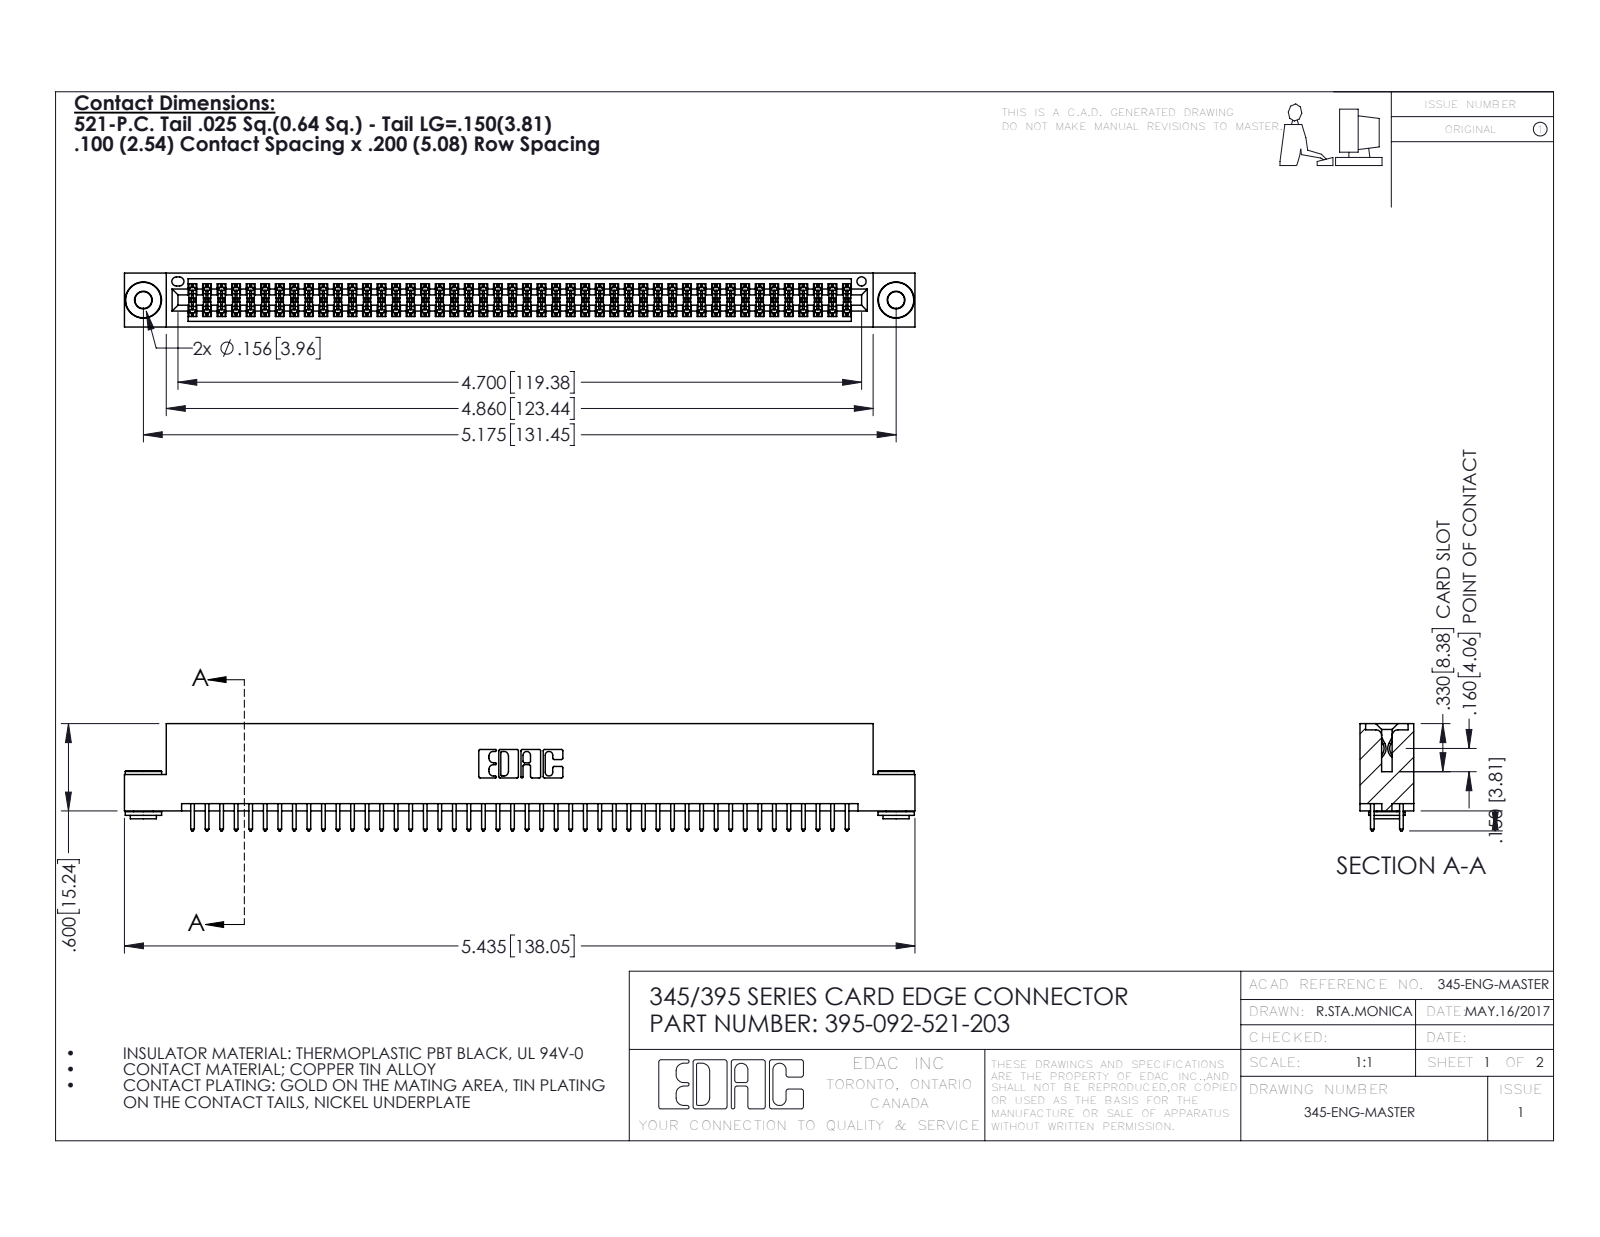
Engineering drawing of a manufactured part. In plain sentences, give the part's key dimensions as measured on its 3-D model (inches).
The part is named "345 Part_Flush Mounting Lugs - 0.156 Dia-TH; 345-250-002_345-250-002-102; 345-292-001_345-293-121; 395-092-521-203". Its 3-D file was written by "SolidWorks 2016 (CONFIG_CONTROL_DESIGN)". It is 95 solids with 4764 faces: 3126 planar, 1630 cylindrical and 8 other. Overall it measures 5.435 by 0.737 by 0.37 inches. Its volume is 0.819 cubic inches and its surface area 30.83 square inches. Round holes: 2 of diameter 0.116, 2 of diameter 0.156, 1 of diameter 0.064. Round bosses or shafts: 2 of diameter 0.25, 2 of diameter 0.18, 2 of diameter 0.136. Partial cylindrical surfaces (rounded edges, fillets, slot ends): 138 of radius 0.006, 92 of radius 0.01, 22 of radius 0.01, 6 of radius 0.007, 6 of radius 0.031, 3 of radius 0.026, 2 of radius 0.014, 2 of radius 0.019. The main face-to-face distances are 0.072, 0.298, 0.2, 0.025, 0.37, 0.098, 0.272, 0.225, 0.175, 0.149. The hole center spacings are 0.27, 4.939, 5.175.
